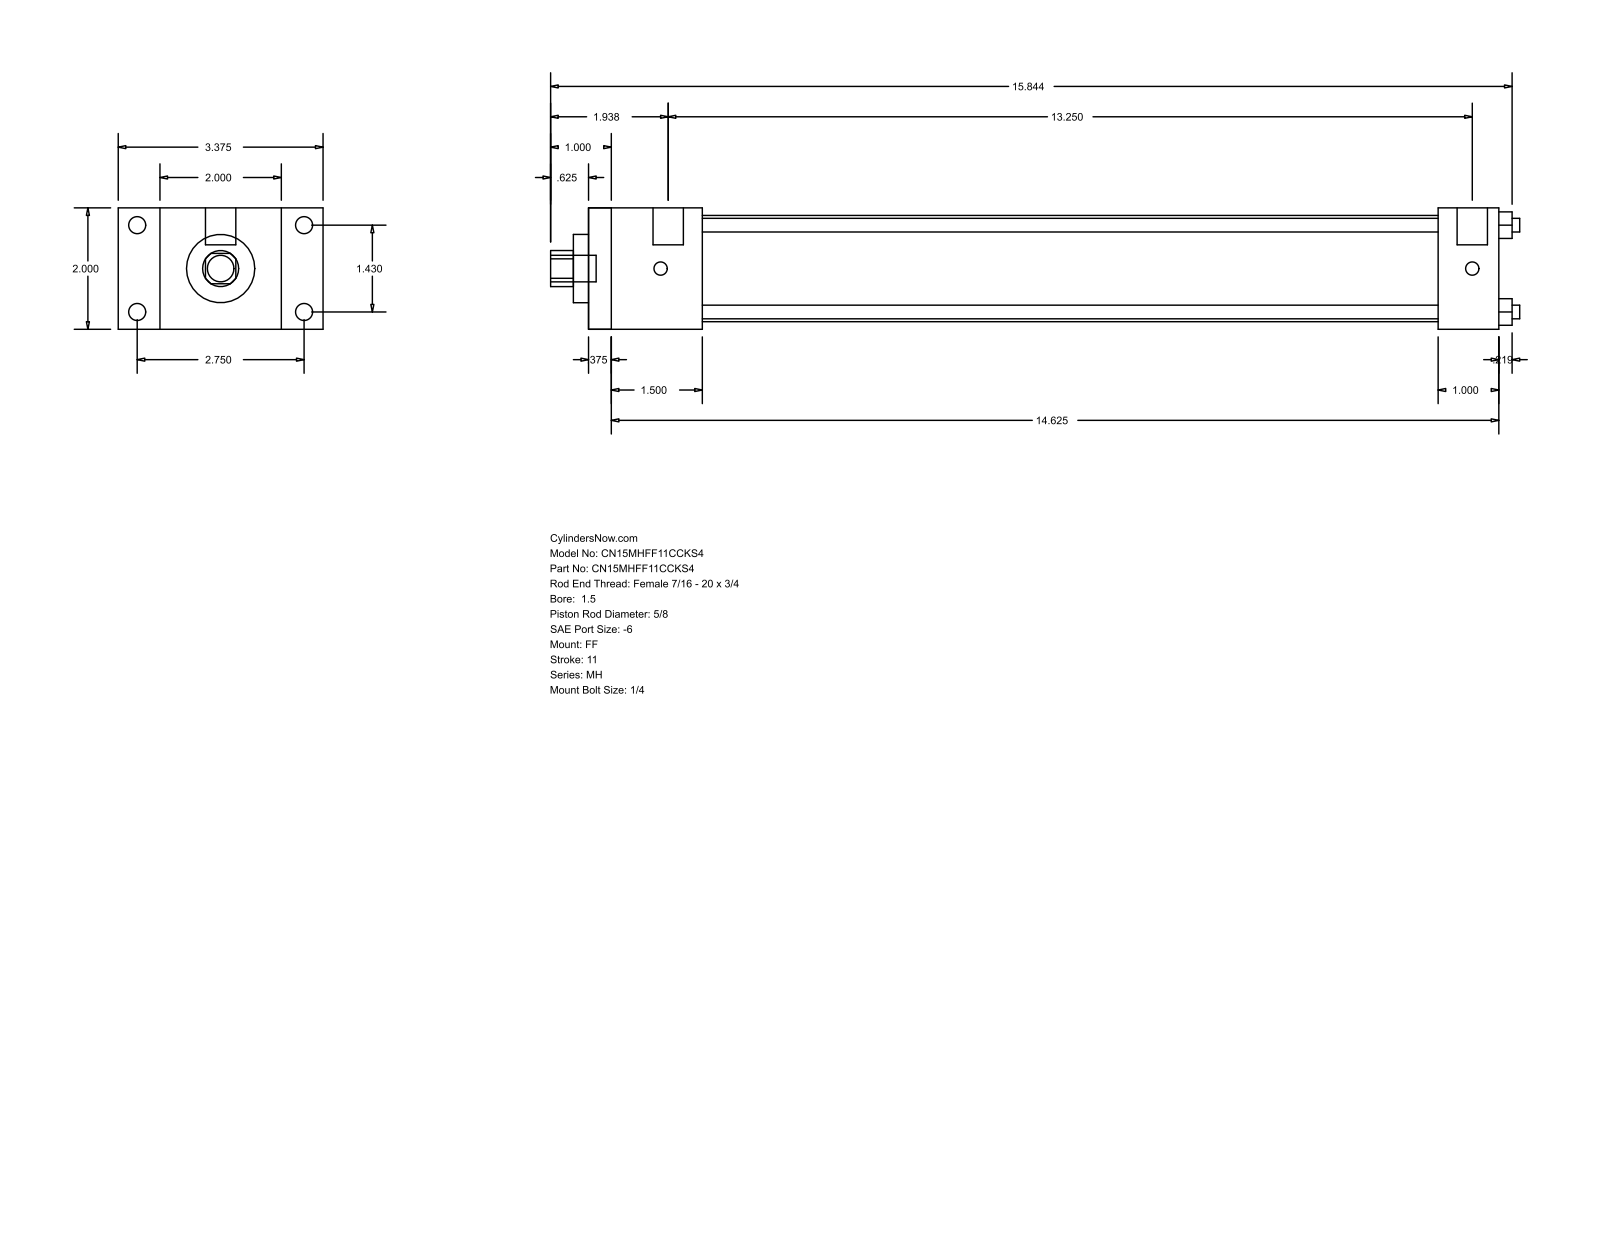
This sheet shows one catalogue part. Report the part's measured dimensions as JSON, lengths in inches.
{"part_name": "MH_FF__0150_0.625", "step_written_by": "GSSL Pune (CONFIG_CONTROL_DESIGN)", "units": "inches", "bodies": {"solids": 0, "faces": 92, "planar": 64, "cylindrical": 28, "other": 0}, "overall_size": [15.969, 3.375, 2], "round_holes": [[0.225, 4], [0.625, 1], [1.125, 1], [1.75, 1]], "round_bosses_or_shafts": [[0.281, 4], [0.219, 4], [0.5, 2], [0.437, 1]], "partial_cylinders_radius": [[0.297, 1]], "face_to_face_distances": [2, 15, 0.375, 14.625, 1, 0.687, 2.687, 1.875, 1.5, 13.125], "hole_center_spacings": [1.011, 1.43, 2.022]}
